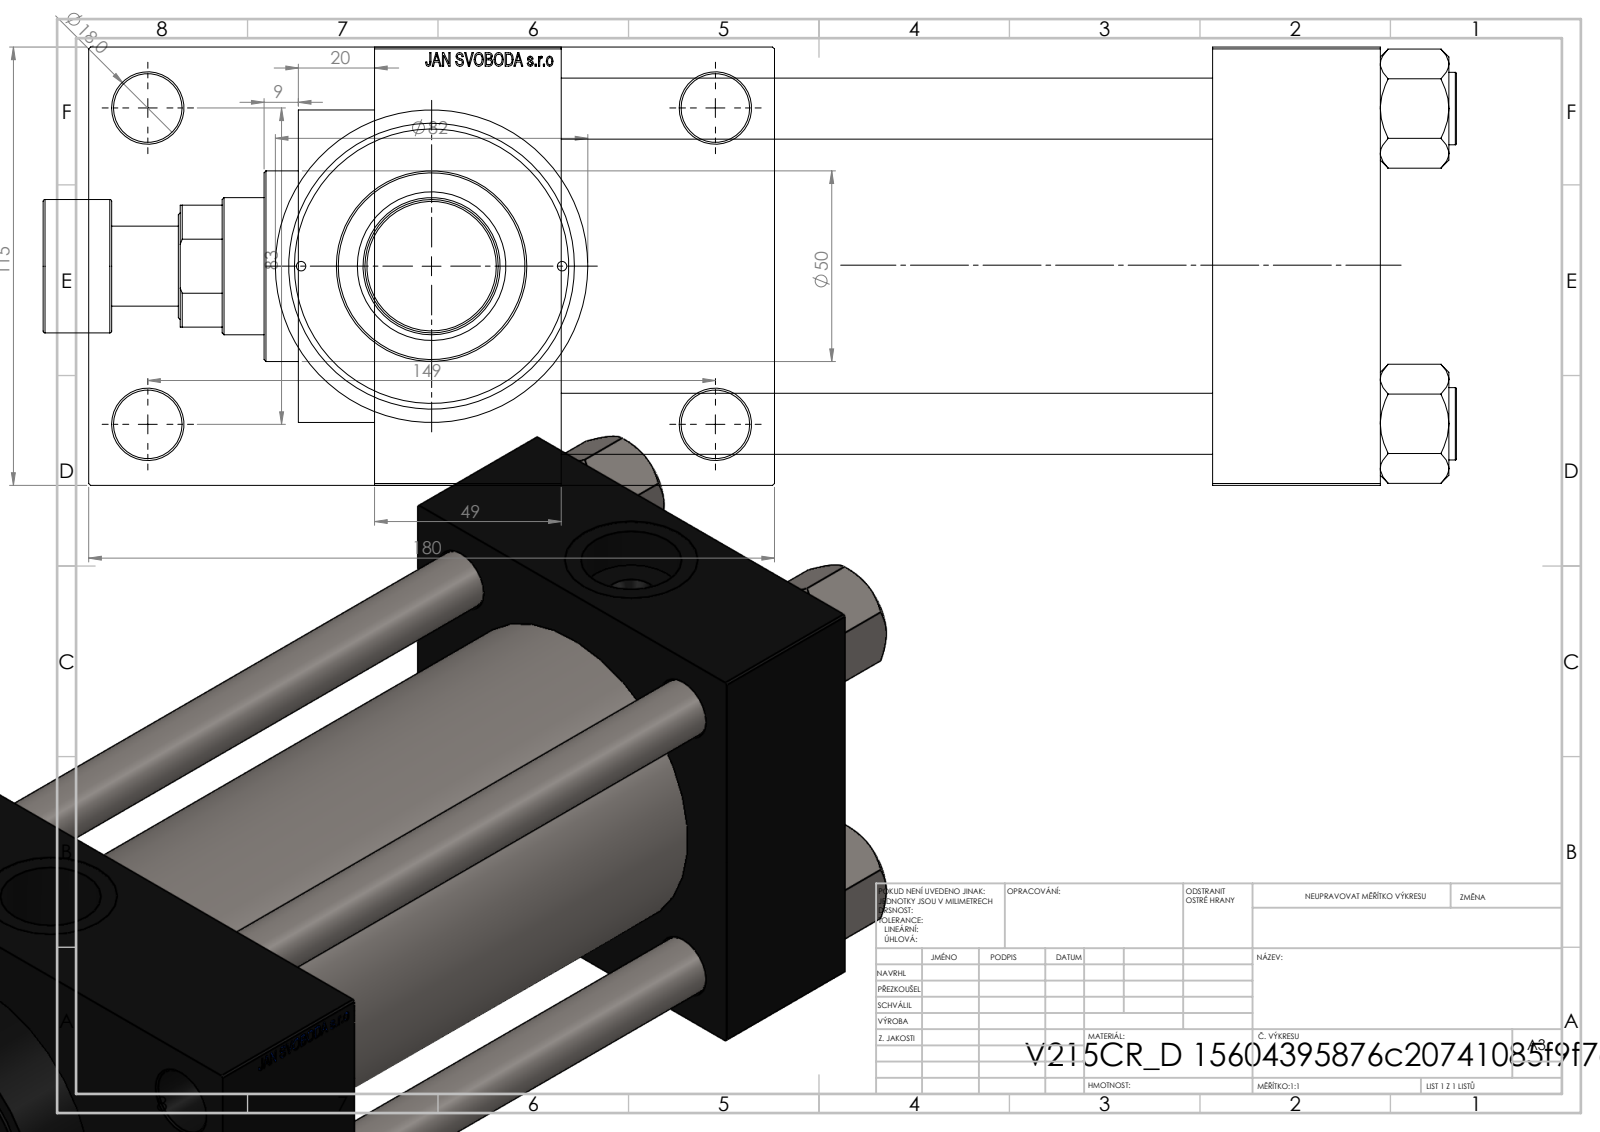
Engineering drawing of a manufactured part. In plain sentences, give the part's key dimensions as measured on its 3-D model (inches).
The part is named "V215CR_VCP_D; V215CR_ROD_END_F; NUT_M5_D; V215CR_D_TYCINKA (+2 more)". Its 3-D file was written by "SolidWorks 2019 (CONFIG_CONTROL_DESIGN)". It is 12 solids with 1174 faces: 551 planar, 97 cylindrical and 526 other. Overall it measures 14.606 by 7.087 by 4.528 inches. Its volume is 140 cubic inches and its surface area 600 square inches. Round holes: 4 of diameter 0.63, 4 of diameter 0.709, 2 of diameter 0.098, 2 of diameter 0.276, 2 of diameter 1.041, 2 of diameter 1.378, 1 of diameter 1.004, 1 of diameter 1.417, 1 of diameter 1.535, 1 of diameter 2.402, 1 of diameter 2.835, 1 of diameter 3.15. Round bosses or shafts: 4 of diameter 0.748, 1 of diameter 3.386, 1 of diameter 3.228, 1 of diameter 1.969, 1 of diameter 1.378, 1 of diameter 0.827. The main face-to-face distances are 4.528, 6.732, 1.929, 8.661, 1.732, 8.465, 10.394, 1.28, 5.807, 7.087. The hole center spacings are 1.305, 1.652, 2.276, 2.302, 3.256, 3.357, 3.393, 3.513.
